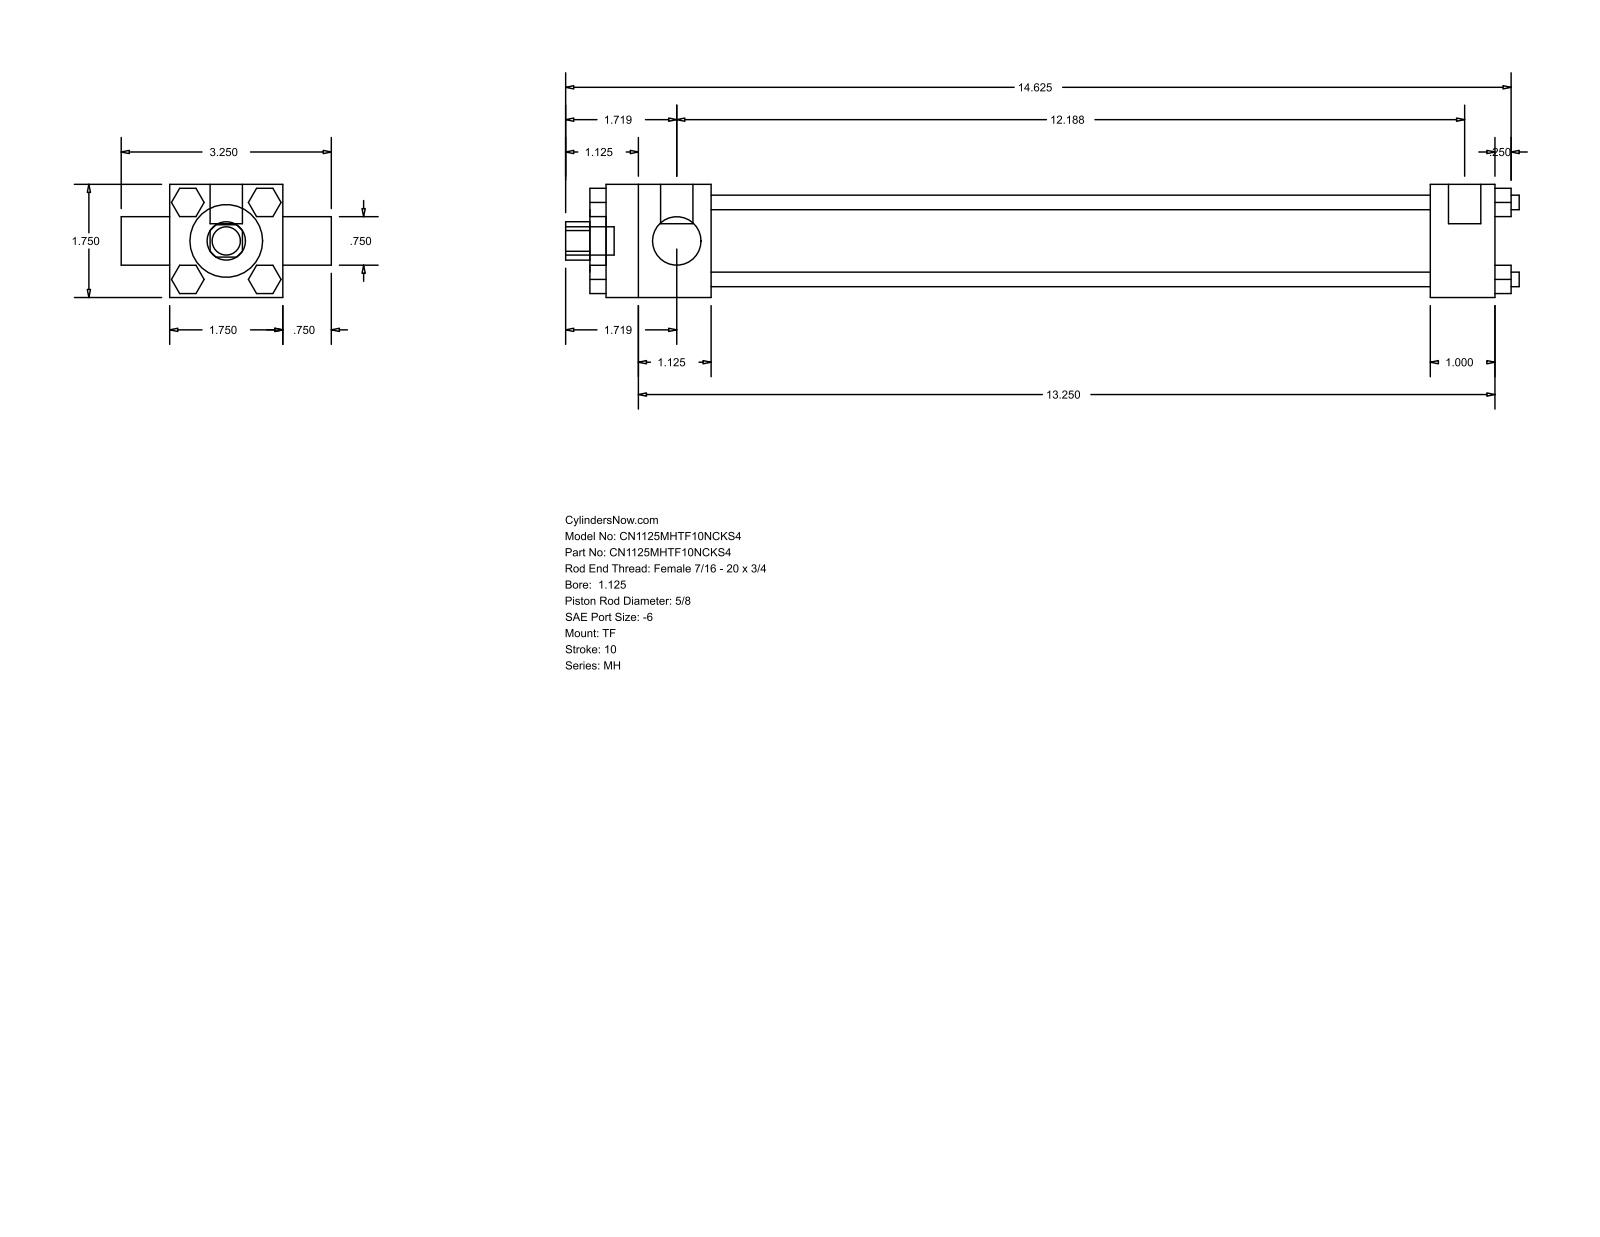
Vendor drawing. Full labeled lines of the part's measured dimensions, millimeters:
Part name (STEP PRODUCT): MH_TF__0112_0.625
STEP written by: GSSL Pune (CONFIG_CONTROL_DESIGN)
Units: millimetres
Bodies: 0 solids, 120 faces (92 planar, 28 cylindrical, 0 other)
Overall size (bounding box): 374.65 × 82.55 × 44.45
Round holes (diameter × count): ⌀15.88 ×1, ⌀19.05 ×1, ⌀28.57 ×1, ⌀34.92 ×1
Round bosses / shafts (diameter × count): ⌀5.71 ×4, ⌀5.56 ×3, ⌀12.7 ×2, ⌀11.11 ×1
Partial cylindrical surfaces — rounded edges, fillets, slot ends (radius × count): R7.54 ×1
Main face-to-face distances: 44.46, 11.11, 282.58, 307.97, 25.39, 41.27, 323.85, 349.24, 47.62, 6.35
